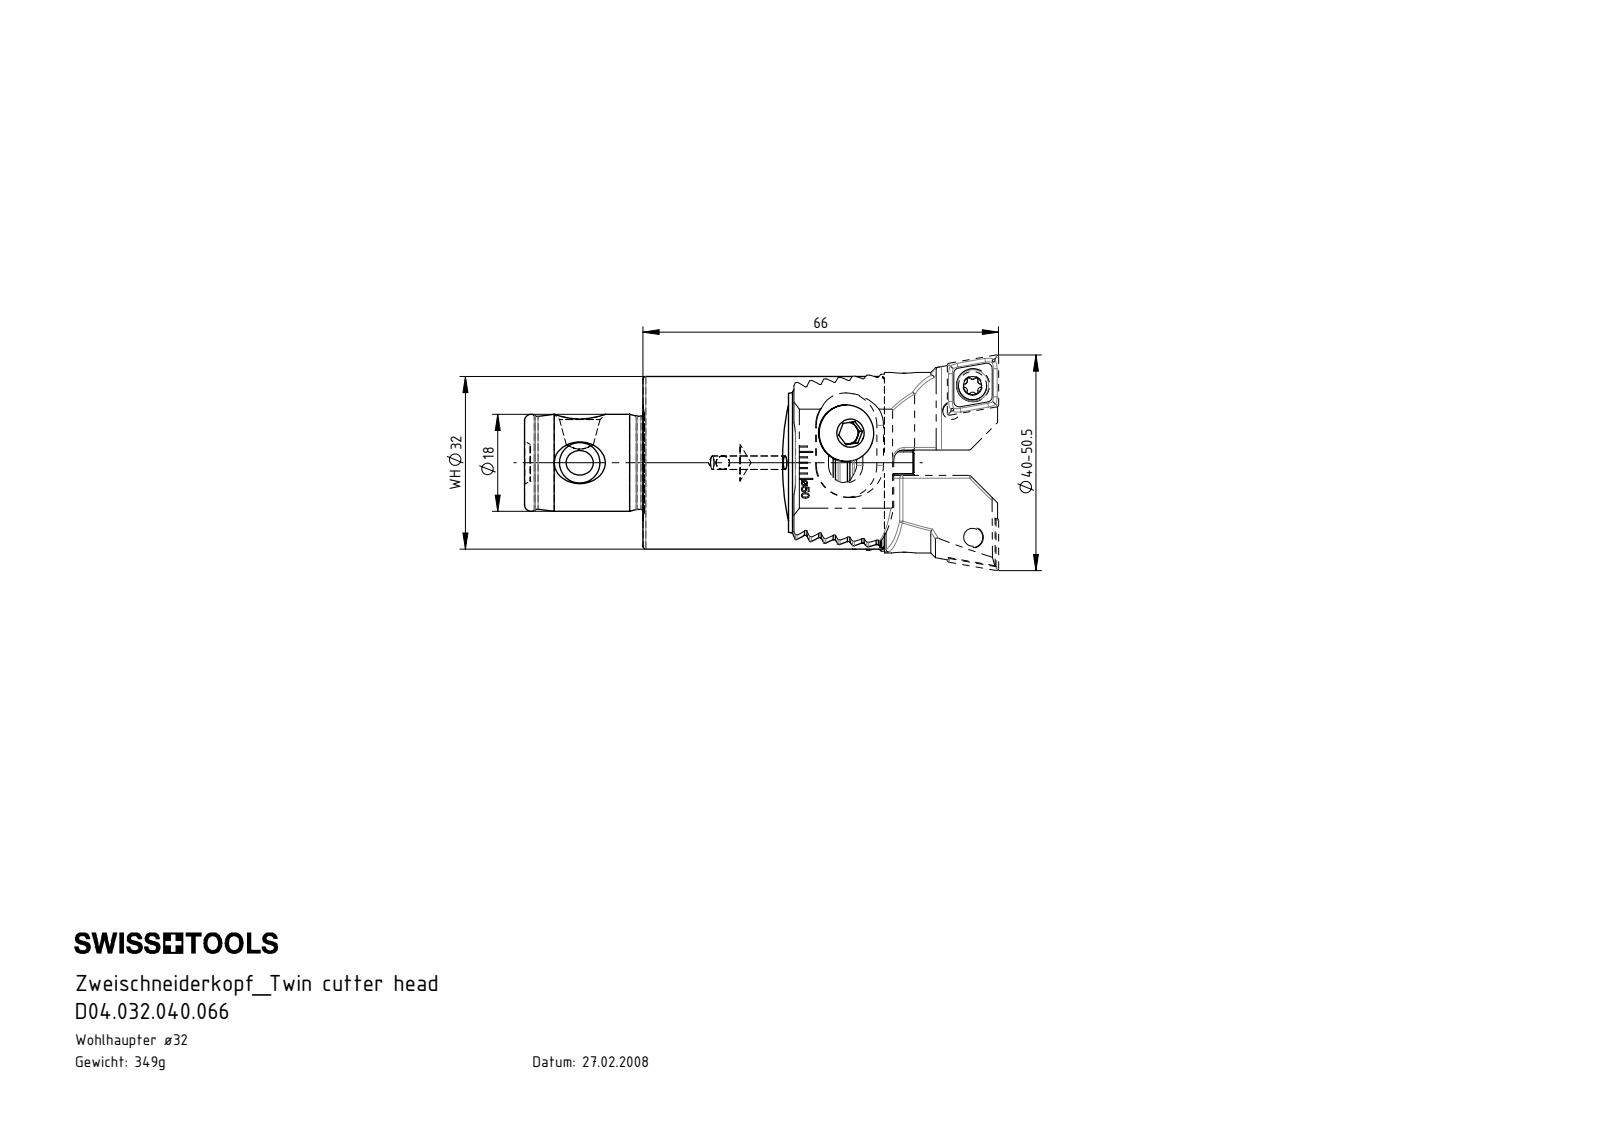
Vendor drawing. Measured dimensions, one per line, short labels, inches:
name: WH3-Z32.K23.066_A; D04.032.040.066; Z32-ER1.003.016_A_gespannt; Z32-WCB.001.021 (+7 more)
written by: SolidWorks 2015 (AUTOMOTIVE_DESIGN)
unit: in
bodies: 14 solids, 934 faces (427 planar, 217 cylindrical, 290 other)
size: 3.465 × 1.575 × 1.26
volume: 2.716 in³; area: 29.21 in²
holes: 4× ⌀0.098, 4× ⌀0.13, 3× ⌀0.268, 2× ⌀0.063, 2× ⌀0.173, 2× ⌀0.197, 2× ⌀0.24, 2× ⌀0.252, 1× ⌀0.138
bosses: 4× ⌀0.157, 2× ⌀0.413, 2× ⌀0.402, 2× ⌀0.236, 2× ⌀0.207, 1× ⌀1.26, 1× ⌀0.709, 1× ⌀0.681
rounds: 16× R0.02, 14× R0.008, 12× R0.008, 12× R0.013, 12× R0.023, 4× R0.079, 4× R0.13, 4× R0.236
face distances: 0.094, 0.187, 0.375, 0.281, 0.095, 0.092, 0.188, 0.469, 0.189, 0.28
hole spacings: 0.239, 0.244, 0.354, 0.954, 0.958, 1.128, 0.684, 0.759
